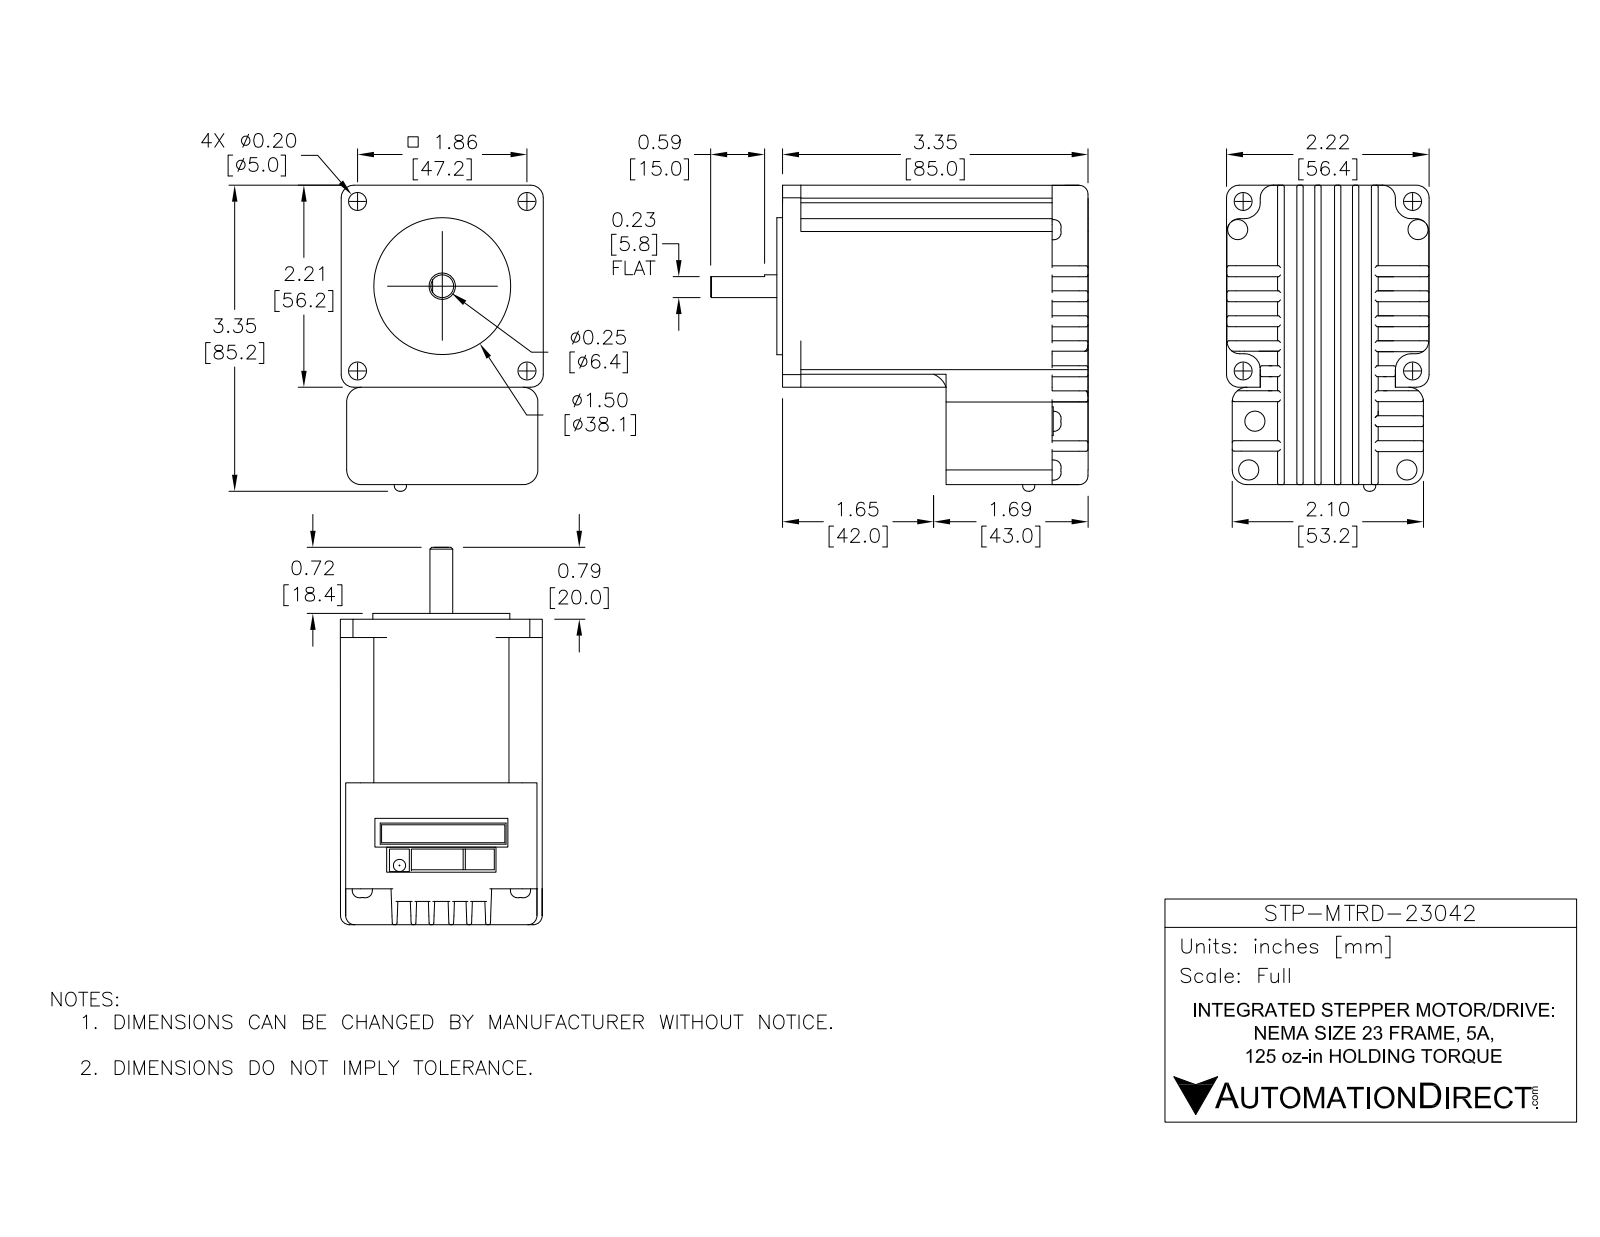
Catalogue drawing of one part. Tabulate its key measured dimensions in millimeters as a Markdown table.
| quantity | value |
| --- | --- |
| part name | STP-MTRD-23042 |
| STEP written by | SolidWorks 2017 (AUTOMOTIVE_DESIGN) |
| units | millimeters |
| bodies | 1 solid, 656 faces (282 planar, 253 cylindrical, 121 other) |
| overall size | 105 × 84.8 × 56.2 |
| volume | 273 683 mm³ |
| surface area | 40 650 mm² |
| round holes (diameter × count) | 5 × 4, 2 × 1, 7.35 × 1 |
| round bosses / shafts (diameter × count) | 5.6 × 5, 5.5 × 4, 38.1 × 1, 8 × 1, 6.35 × 1 |
| partial cylindrical surfaces (radius × count) | 0.5 × 87, 2.5 × 10, 3.6 × 8, 0.68 × 5, 10.96 × 5, 3.2 × 4, 3.5 × 4, 4.1 × 4 |
| main face-to-face distances | 56.2, 4.99, 10.49, 5.25, 15.74, 20.73, 10.24, 78.5, 33, 45.5 |
| hole center spacings | 33.33, 47.14, 66.67 |
